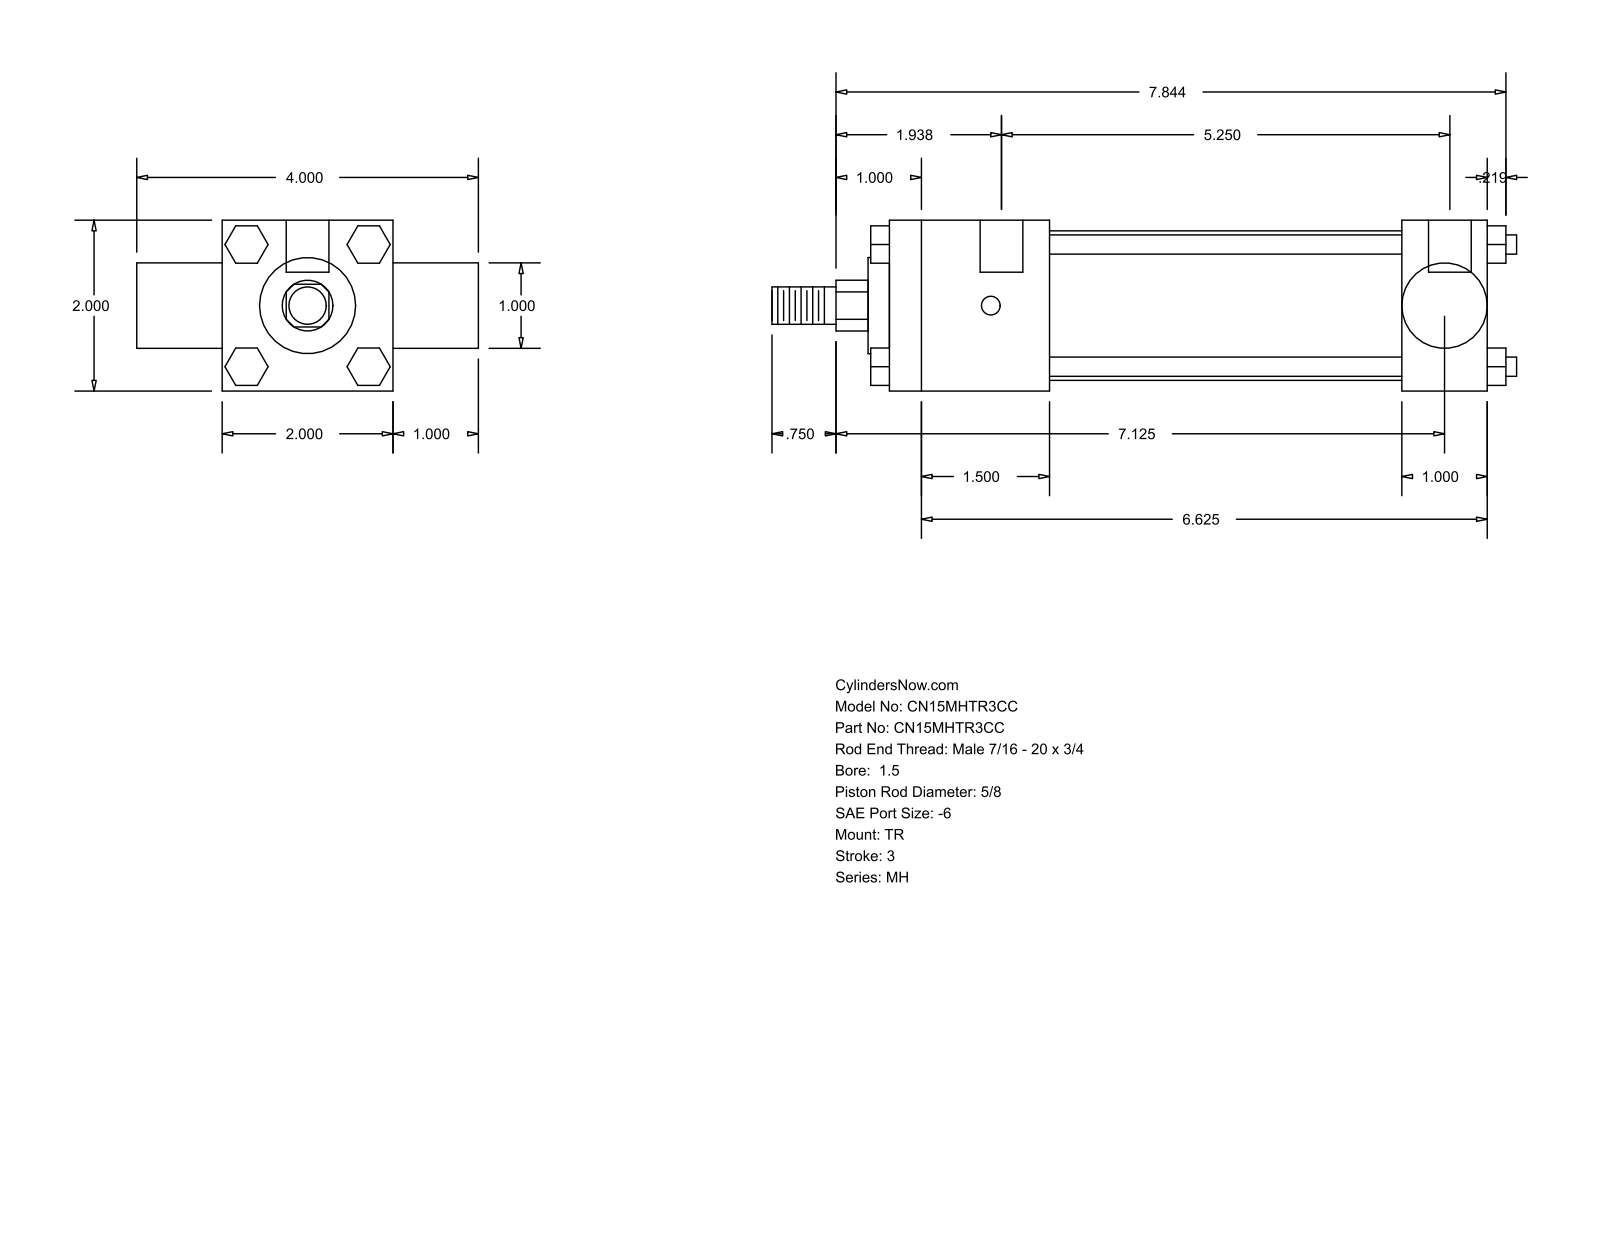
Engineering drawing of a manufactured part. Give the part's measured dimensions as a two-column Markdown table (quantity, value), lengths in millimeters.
| quantity | value |
| --- | --- |
| part name | MH_TR__0150_0.625 |
| STEP written by | GSSL Pune (CONFIG_CONTROL_DESIGN) |
| units | millimeters |
| bodies | 0 solids, 120 faces (92 planar, 28 cylindrical, 0 other) |
| overall size | 221.46 × 101.6 × 50.8 |
| round holes (diameter × count) | 5.56 × 3, 12.7 × 2 |
| round bosses / shafts (diameter × count) | 5.71 × 4, 44.45 × 1, 28.57 × 1, 25.35 × 1, 15.88 × 1, 11.11 × 1 |
| partial cylindrical surfaces (radius × count) | 7.54 × 1 |
| main face-to-face distances | 50.8, 25.4, 177.8, 76.2, 47.62, 130.18, 152.4, 104.78, 11.11, 18.16 |
| hole center spacings | 3.17, 133.35, 136.52 |
